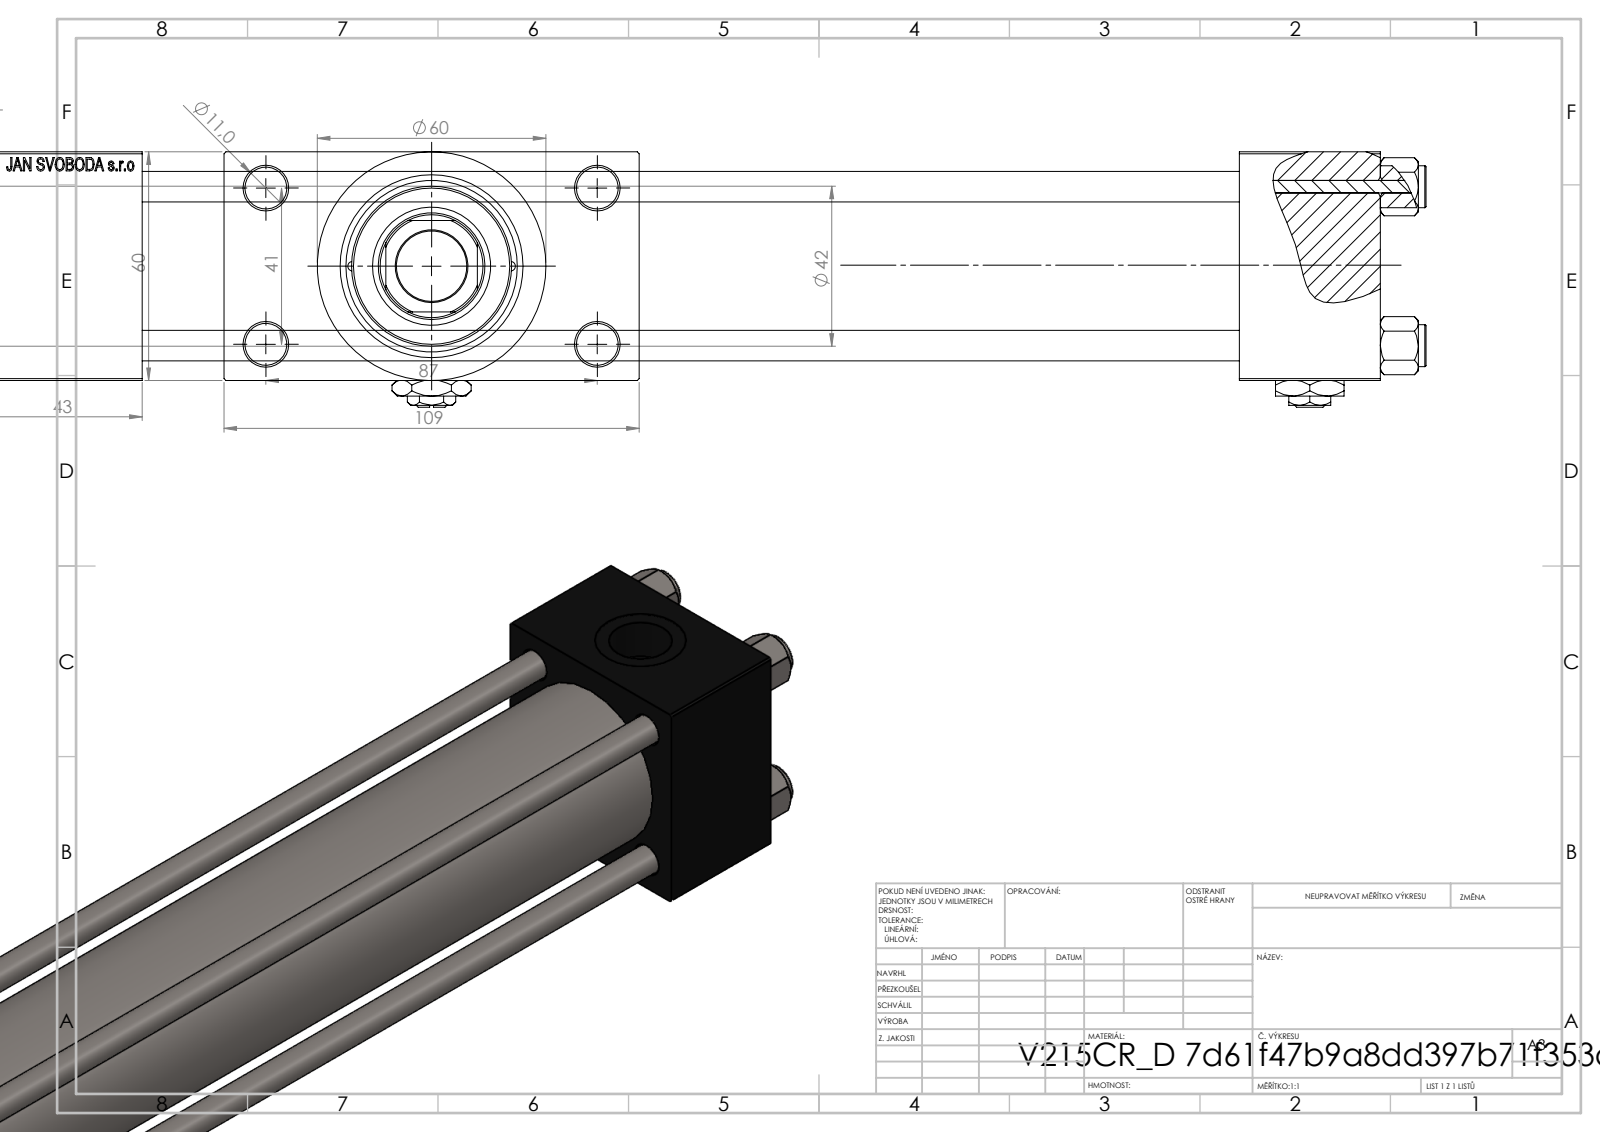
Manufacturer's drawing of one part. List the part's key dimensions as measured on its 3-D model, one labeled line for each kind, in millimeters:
Part name (STEP PRODUCT): V215CR_D_Body; V215CR_D_TYCINKA; V215CR_VCP_D; Zatka_pro_OIL_PORT (+2 more)
STEP written by: SolidWorks 2019 (CONFIG_CONTROL_DESIGN)
Units: millimetres
Bodies: 12 solids, 1168 faces (526 planar, 100 cylindrical, 542 other)
Overall size (bounding box): 415 × 109 × 67
Volume: 813 246 mm³ · Surface area: 235 027 mm²
Round holes (diameter × count): ⌀8 ×4, ⌀11 ×4, ⌀2.5 ×2, ⌀7 ×2, ⌀16.66 ×2, ⌀24 ×2, ⌀18.5 ×1, ⌀28 ×1, ⌀31 ×1, ⌀40 ×1, ⌀45 ×1
Round bosses / shafts (diameter × count): ⌀11 ×4, ⌀60 ×1, ⌀46 ×1, ⌀42 ×1
Partial cylindrical surfaces — rounded edges, fillets, slot ends (radius × count): R13.5 ×1
Main face-to-face distances: 60, 24.5, 84.5, 288, 37, 325, 368, 331, 43, 109
Hole centre spacings: 20.85, 22.65, 29.49, 30.62, 41.7, 46.53, 47.15, 48.09
